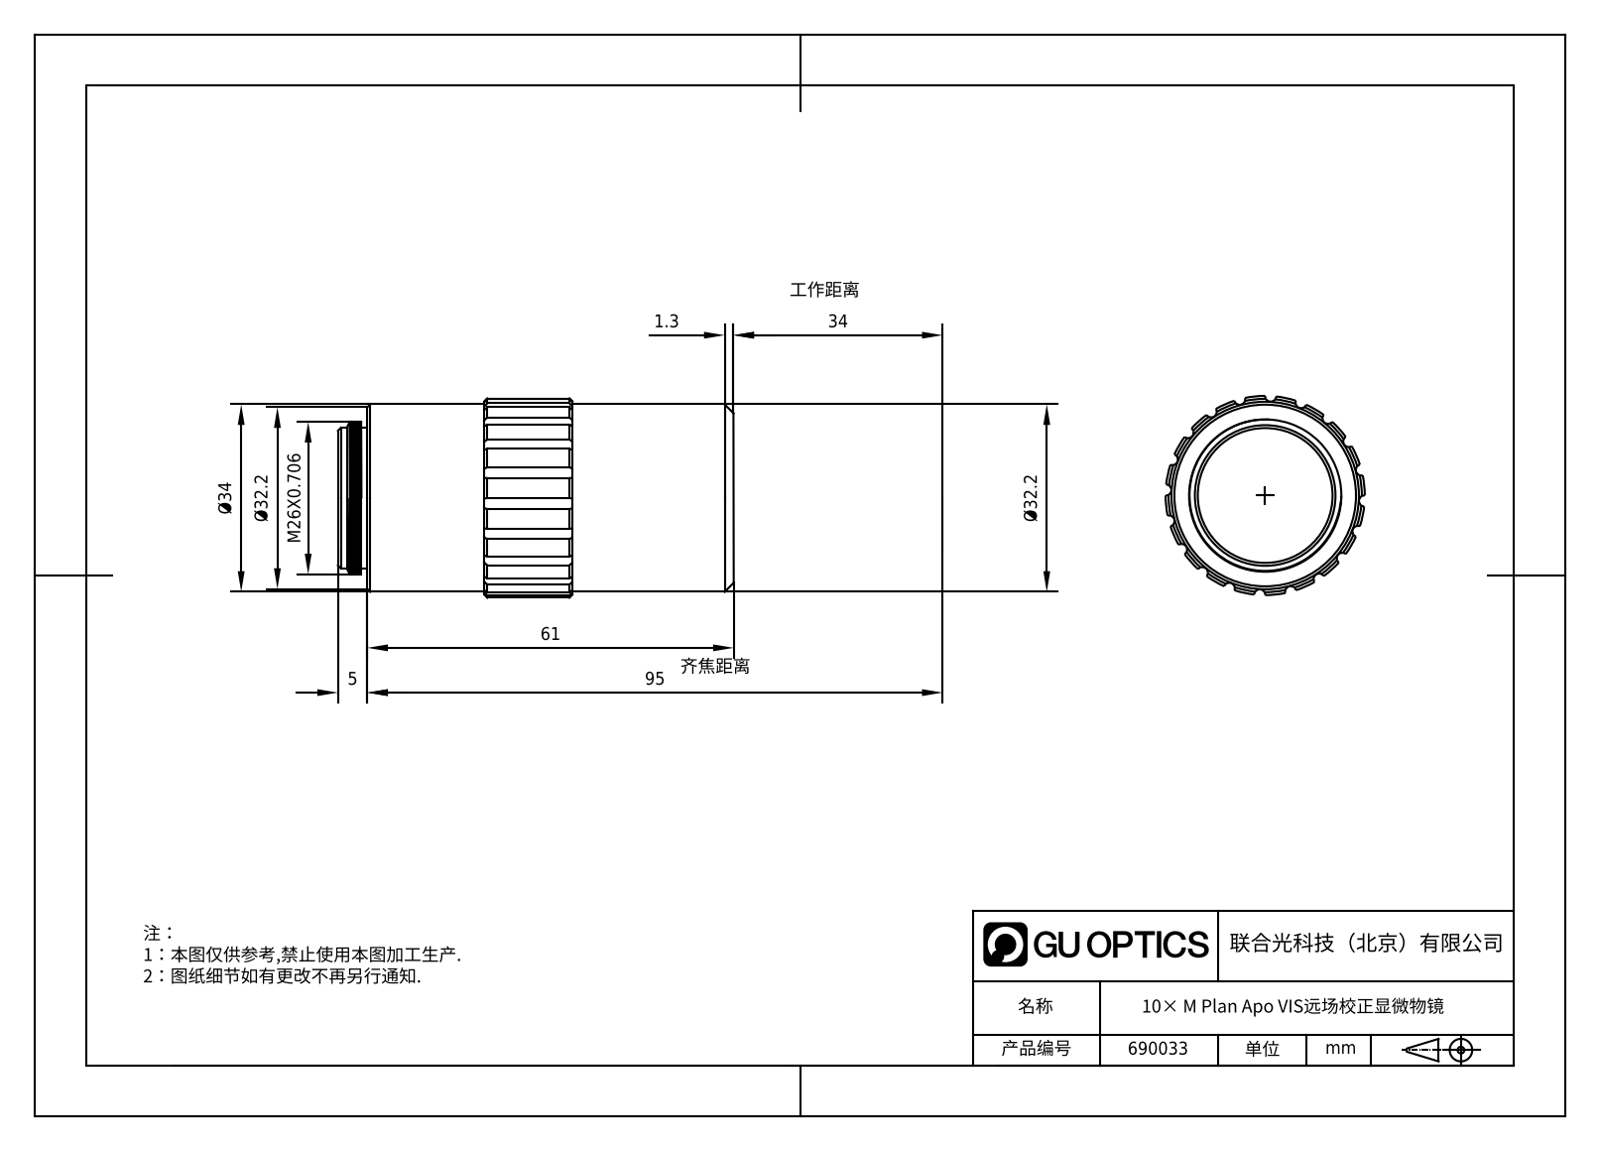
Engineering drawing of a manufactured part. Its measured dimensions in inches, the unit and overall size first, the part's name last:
Units: inches
Overall size (bounding box): 2.626 × 1.337 × 1.337
Round bosses / shafts (diameter × count): ⌀1.266 ×1, ⌀1.26 ×1, ⌀1.024 ×1, ⌀0.945 ×1
Partial cylindrical surfaces — rounded edges, fillets, slot ends (radius × count): R0.028 ×16, R0.63 ×1, R0.669 ×1
Main face-to-face distances: 0.309, 2.514, 2.205, 2.317, 2.008, 0.197, 0.085, 0.394, 2.402, 2.598
Volume: 2.992 in³ · Surface area: 21.84 in²
Bodies: 4 solids, 307 faces (132 planar, 79 cylindrical, 96 other)
Part name (STEP PRODUCT): 690033
STEP written by: SolidWorks 2020 (CONFIG_CONTROL_DESIGN)
